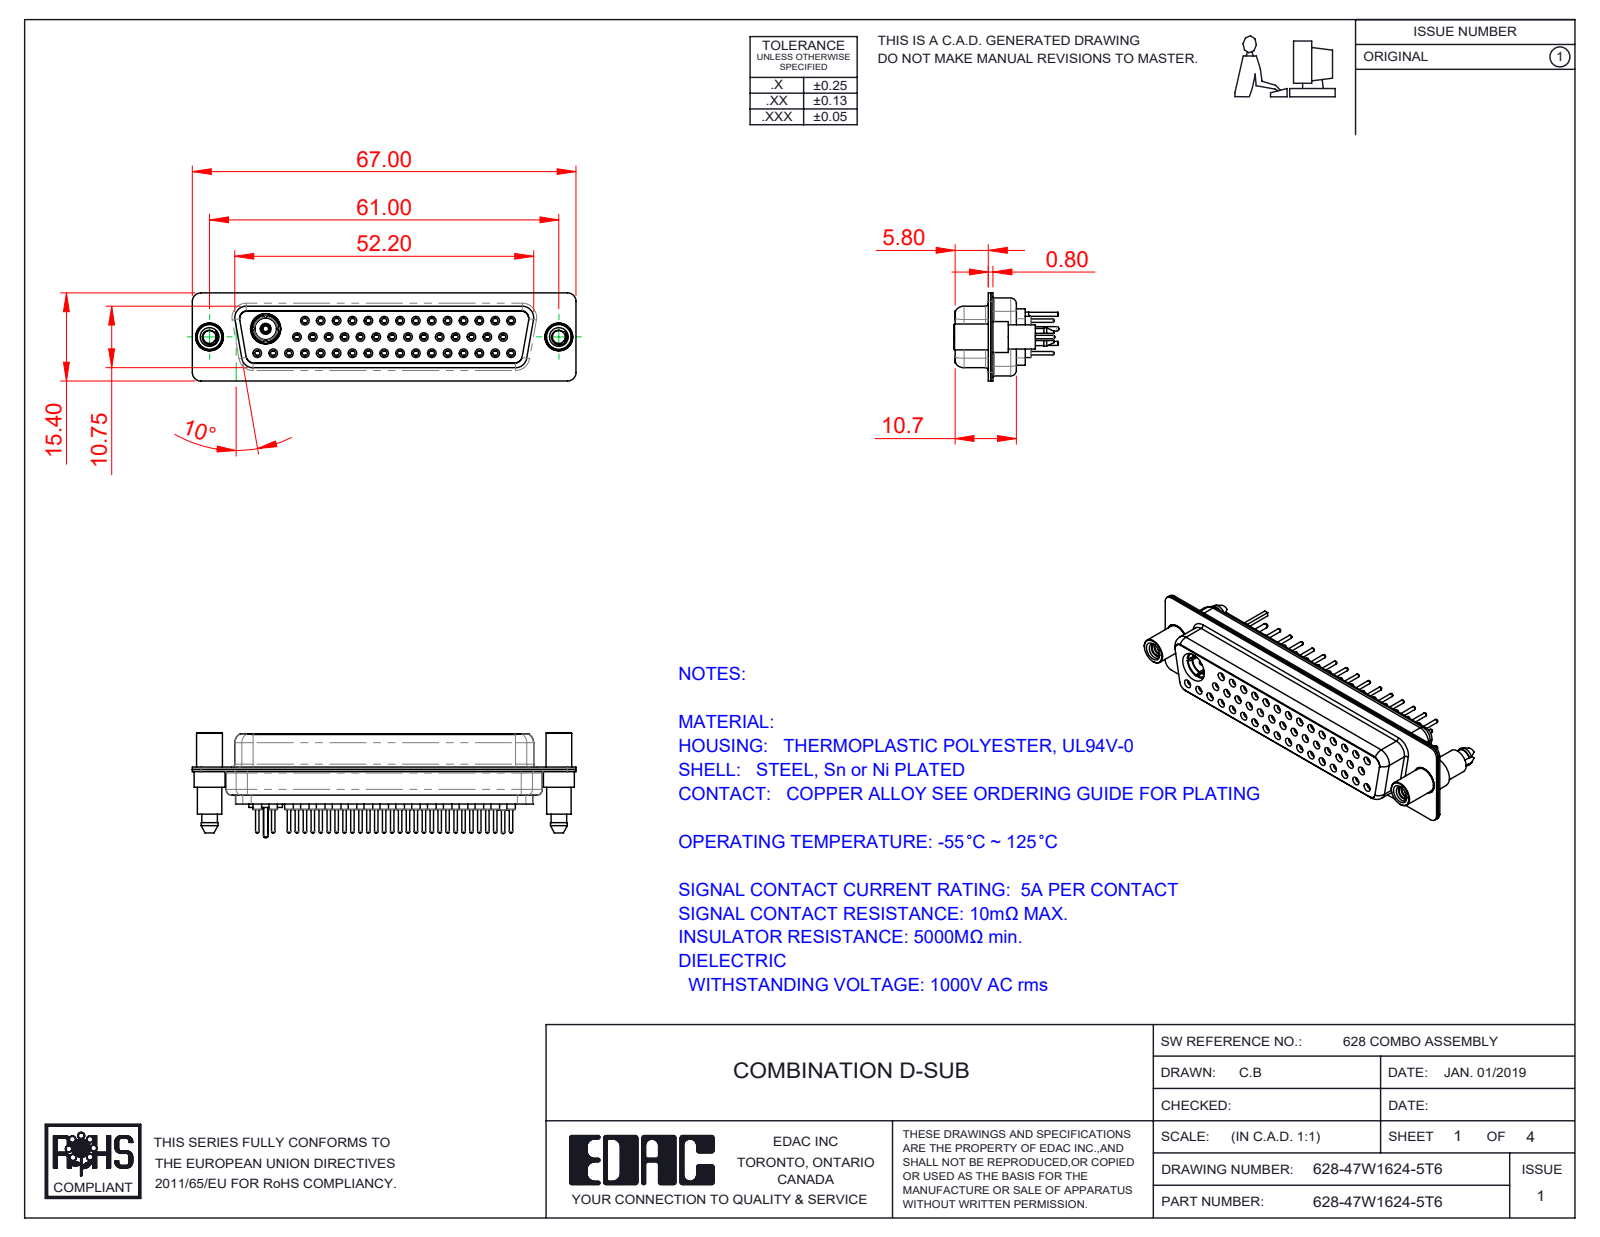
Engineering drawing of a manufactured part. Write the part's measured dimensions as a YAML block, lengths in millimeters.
part_name: "628Combo Shell Rear_50 Contacts; Insulator Pin_Straight PC Tail; 628Combo Shell Front_50 Contacts; 628Combo Contact Row 3_24 (+8 more)"
step_written_by: "SolidWorks 2016 (CONFIG_CONTROL_DESIGN)"
units: millimeters
bodies: {solids: 55, faces: 2975, planar: 829, cylindrical: 1076, other: 1070}
overall_size: [67, 18.35, 15.4]
volume: 7383
surface_area: 15348
round_holes:
  - {diameter: 1.1, count: 47}
  - {diameter: 1.5, count: 46}
  - {diameter: 0.9, count: 45}
  - {diameter: 2, count: 45}
  - {diameter: 1.6, count: 31}
  - {diameter: 1.7, count: 14}
  - {diameter: 4.85, count: 3}
  - {diameter: 2.26, count: 2}
  - {diameter: 4, count: 2}
  - {diameter: 4.05, count: 2}
  - {diameter: 2.83, count: 1}
  - {diameter: 3.3, count: 1}
round_bosses_or_shafts:
  - {diameter: 2.2, count: 46}
  - {diameter: 0.6, count: 46}
  - {diameter: 1.6, count: 15}
  - {diameter: 5.4, count: 2}
  - {diameter: 4.95, count: 2}
  - {diameter: 4.8, count: 2}
  - {diameter: 4.5, count: 2}
  - {diameter: 4.25, count: 2}
partial_cylinders:
  - {radius: 1.5, count: 18}
  - {radius: 1.35, count: 12}
  - {radius: 2, count: 12}
  - {radius: 1.6, count: 10}
  - {radius: 0.25, count: 4}
  - {radius: 0.5, count: 4}
  - {radius: 0.6, count: 4}
  - {radius: 0.65, count: 4}
face_to_face_distances: [0.4, 6.05, 11.33, 6.45, 1.87, 12.25, 6.2, 5.8, 10.35, 10.93]
hole_center_spacings: [3.16, 2.77, 5.54, 8.31, 11.08, 13.85, 16.62, 19.39]
